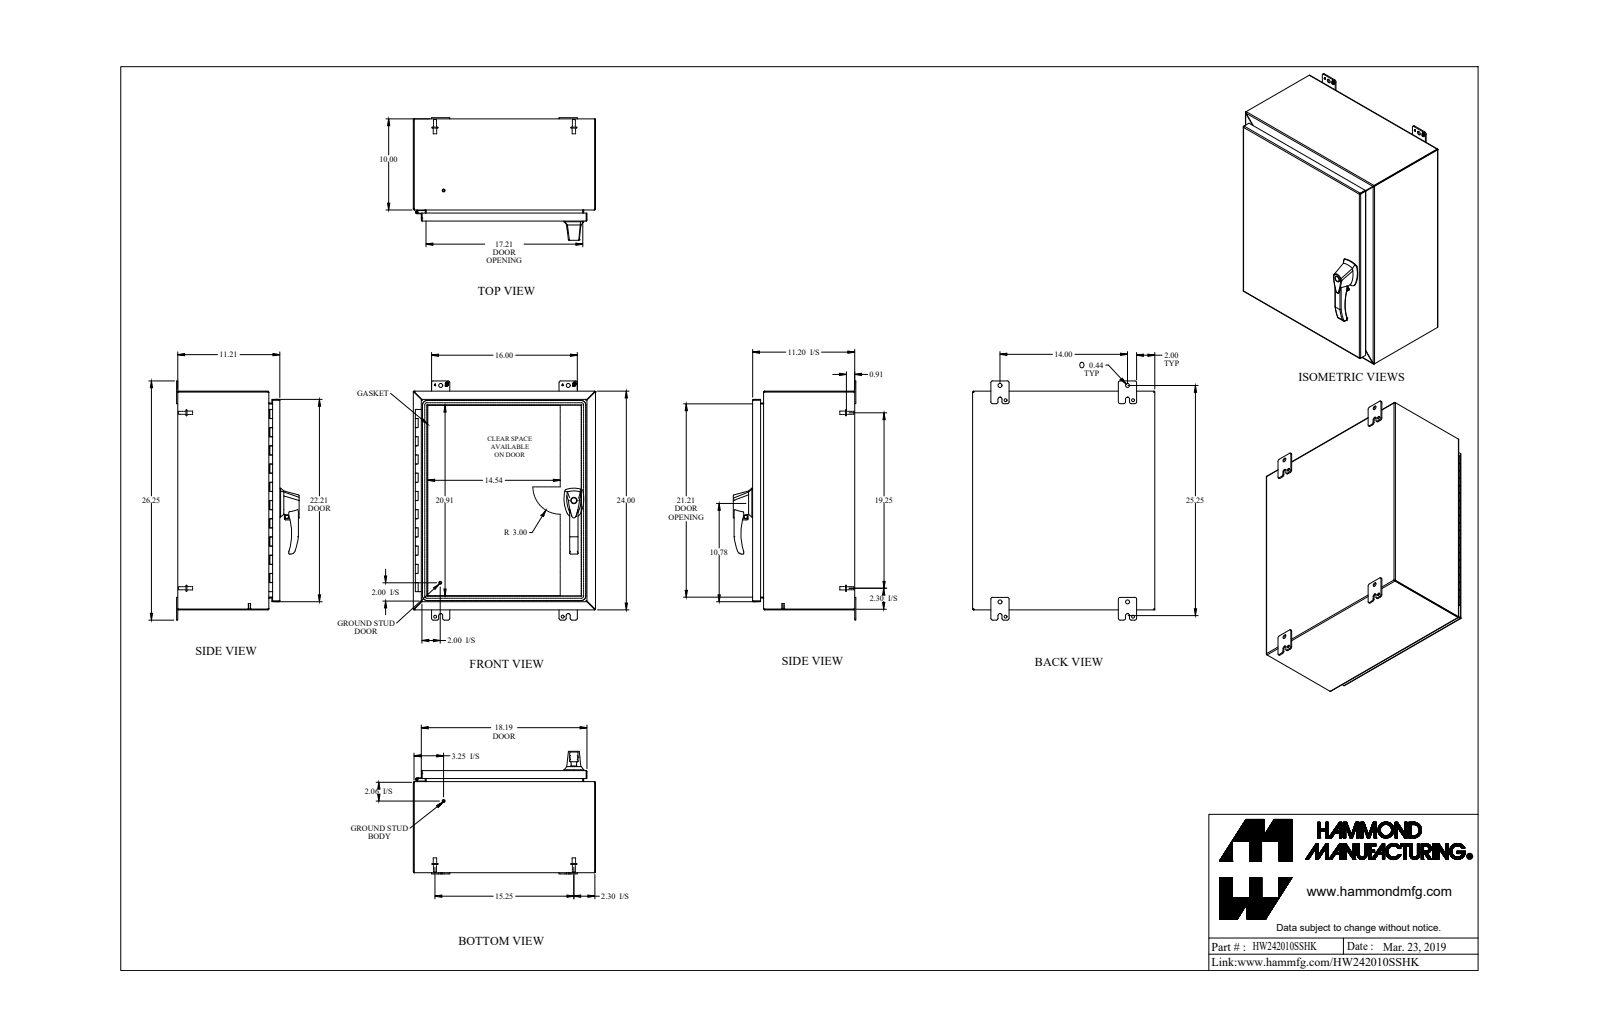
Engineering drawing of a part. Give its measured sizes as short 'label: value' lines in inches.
name: HW242010SSHK
written by: SolidWorks 2018 (AUTOMOTIVE_DESIGN)
unit: in
bodies: 42 solids, 1423 faces (699 planar, 569 cylindrical, 155 other)
size: 26.25 × 20 × 13.45
volume: 178.6 in³; area: 4 566 in²
holes: 6× ⌀0.176, 5× ⌀0.313, 3× ⌀0.25, 3× ⌀0.265, 3× ⌀0.413, 2× ⌀0.196, 2× ⌀0.256, 2× ⌀0.394, 2× ⌀0.437, 1× ⌀0.187, 1× ⌀0.233, 1× ⌀0.33
bosses: 9× ⌀0.375, 7× ⌀0.25, 6× ⌀0.156, 4× ⌀0.65, 4× ⌀0.332, 4× ⌀0.313, 3× ⌀1, 3× ⌀0.51
rounds: 27× R0.25, 24× R0.188, 20× R0.036, 20× R0.108, 12× R0.06, 9× R0.125, 8× R0.045, 8× R0.218
face distances: 0.072, 19.928, 11.138, 11.066, 0.072, 11.138, 11.21, 23.928, 19.856, 20
hole spacings: 1.111, 8.118, 8.119, 16.237, 1.338, 6.78, 7.576, 7.577
